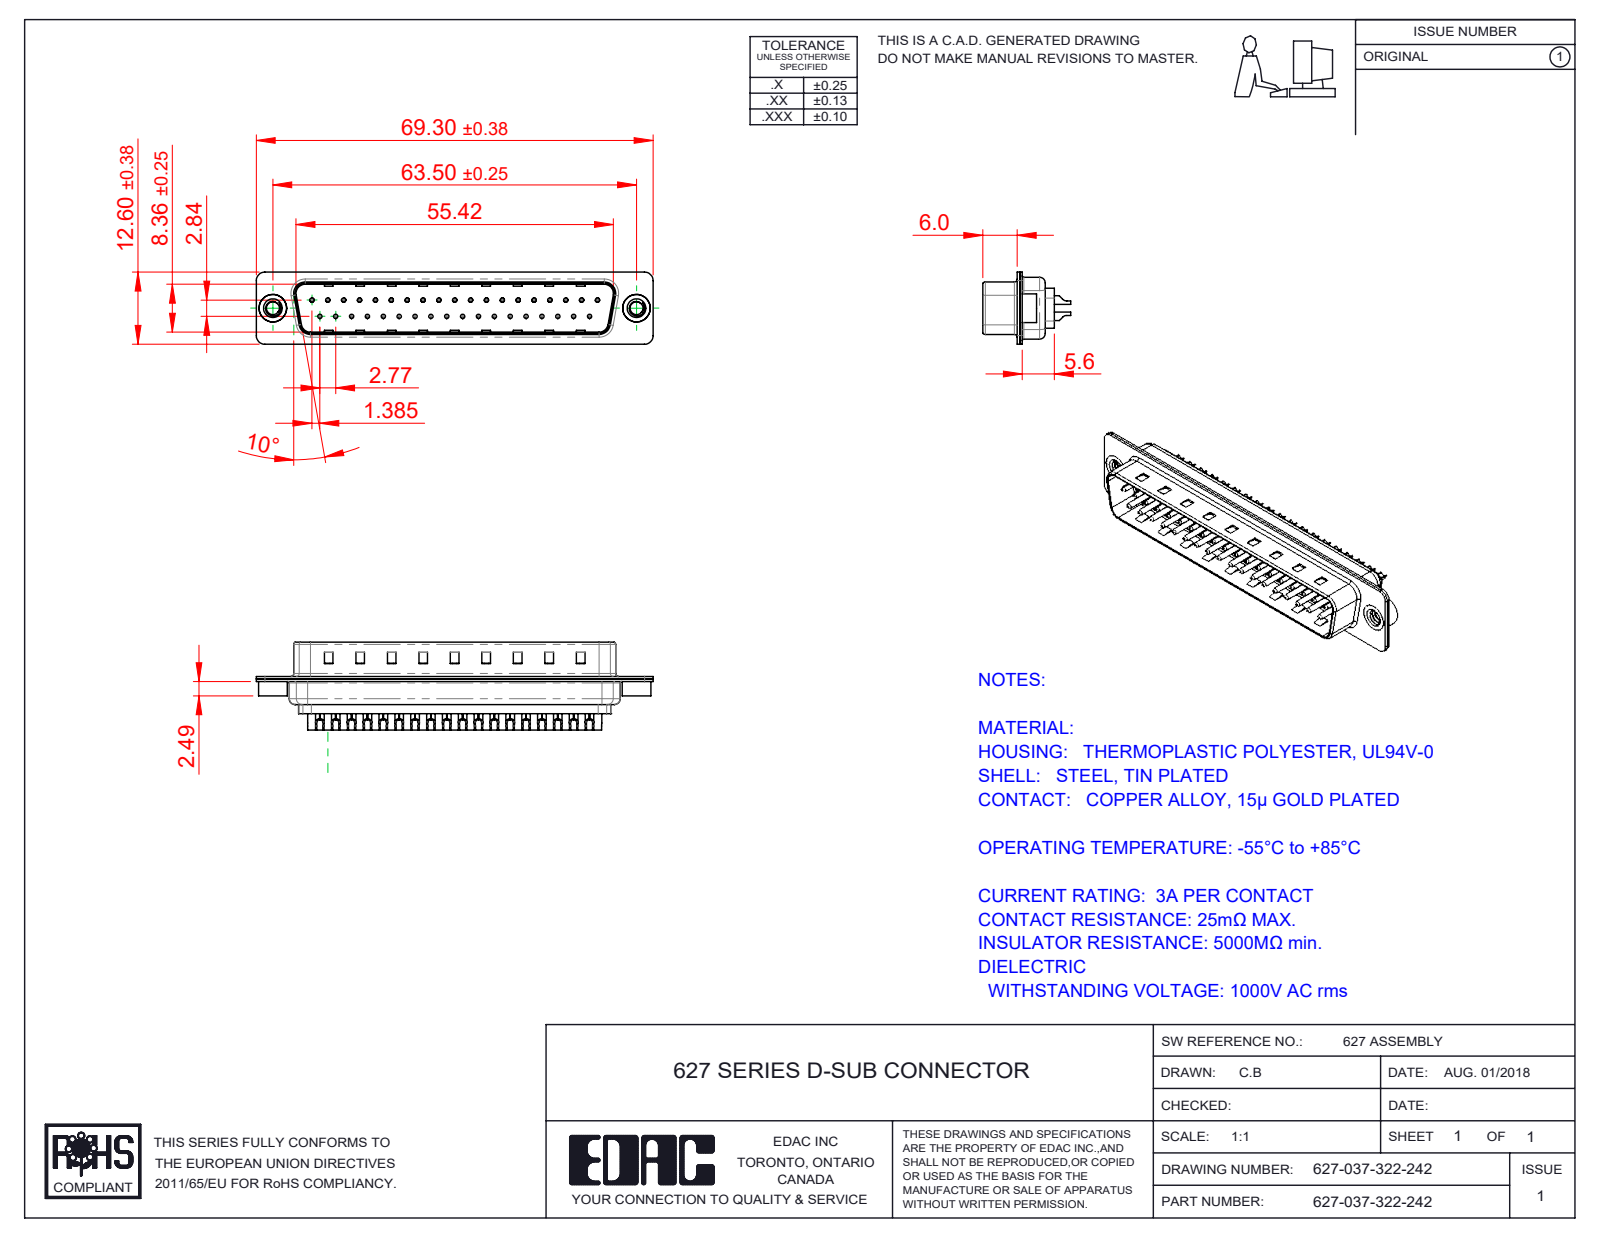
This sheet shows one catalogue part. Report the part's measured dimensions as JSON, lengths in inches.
{"part_name": "627 Housing_37 LP; 627 Contact Row 1_22L; 627 Shell Rear_37 Contacts; 627-037-322-042 (+3 more)", "step_written_by": "SolidWorks 2020 (CONFIG_CONTROL_DESIGN)", "units": "inches", "bodies": {"solids": 42, "faces": 2776, "planar": 721, "cylindrical": 1212, "other": 843}, "overall_size": [2.728, 0.604, 0.496], "volume_in3": 0.226, "surface_area_in2": 16.66, "round_holes": [[0.014, 37], [0.043, 37], [0.063, 37], [0.089, 2], [0.157, 2], [0.189, 2]], "round_bosses_or_shafts": [[0.079, 37], [0.059, 37], [0.03, 37], [0.197, 2], [0.193, 2]], "partial_cylinders_radius": [[0.059, 16], [0.079, 12], [0.02, 8], [0.063, 8], [0.039, 6], [0.01, 4], [0.024, 4], [0.026, 4]], "face_to_face_distances": [0.016, 0.032, 0.377, 0.018, 0.345, 0.059, 0.035, 0.055, 0.238, 0.017], "hole_center_spacings": [0.124, 0.109, 0.218, 0.327, 0.198, 0.398, 0.436, 0.503]}
